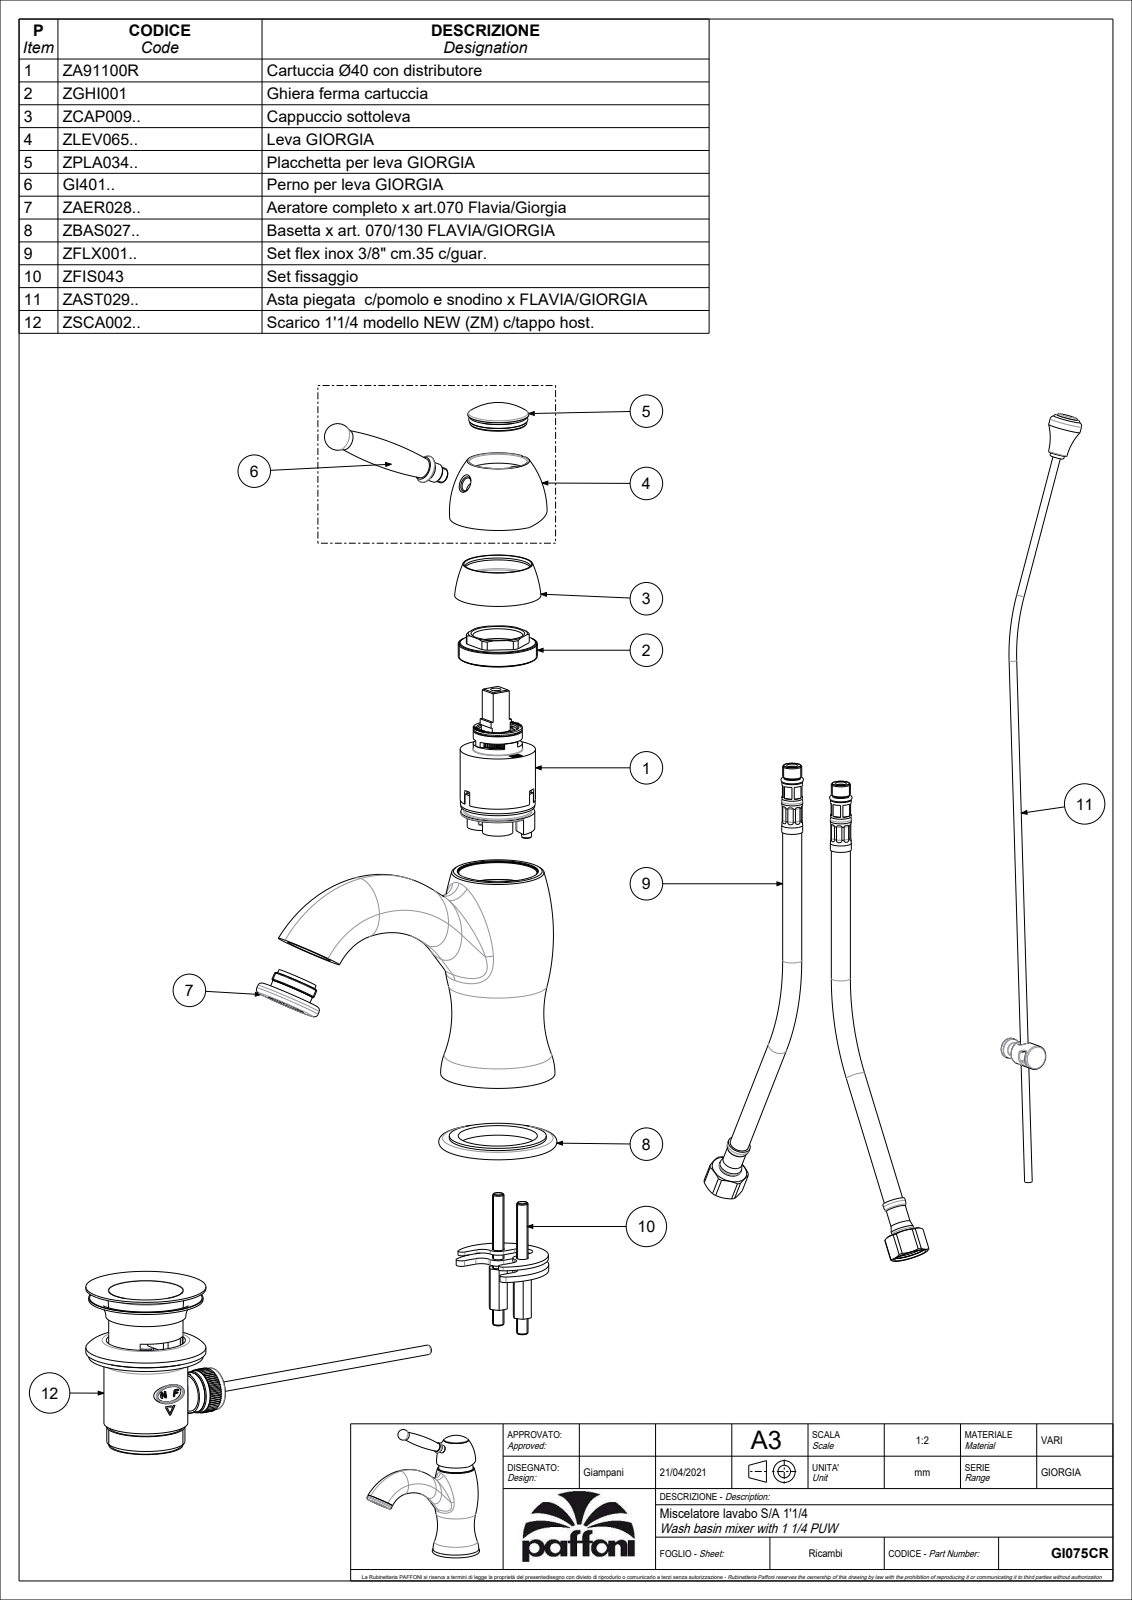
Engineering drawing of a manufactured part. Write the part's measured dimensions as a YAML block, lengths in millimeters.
part_name: "GI075CR"
step_written_by: "CREO PARAMETRIC BY PTC INC, 2020044 (CONFIG_CONTROL_DESIGN)"
units: millimeters
bodies: {solids: 3, faces: 344, planar: 85, cylindrical: 98, other: 161}
overall_size: [185.29, 179.37, 62]
volume: 185842
surface_area: 103906
round_holes:
  - {diameter: 5.5, count: 5}
  - {diameter: 5, count: 4}
  - {diameter: 9, count: 2}
  - {diameter: 11, count: 2}
  - {diameter: 12, count: 1}
  - {diameter: 16, count: 1}
  - {diameter: 20.1, count: 1}
  - {diameter: 21.1, count: 1}
  - {diameter: 23, count: 1}
  - {diameter: 30.3, count: 1}
  - {diameter: 34.5, count: 1}
  - {diameter: 39.1, count: 1}
round_bosses_or_shafts:
  - {diameter: 8.5, count: 2}
  - {diameter: 50.9, count: 1}
  - {diameter: 35, count: 1}
  - {diameter: 32, count: 1}
  - {diameter: 29.9, count: 1}
  - {diameter: 27, count: 1}
  - {diameter: 17.5, count: 1}
  - {diameter: 17, count: 1}
partial_cylinders:
  - {radius: 2.5, count: 2}
  - {radius: 6, count: 2}
  - {radius: 8, count: 2}
  - {radius: 2, count: 1}
  - {radius: 3.5, count: 1}
  - {radius: 24.35, count: 1}
face_to_face_distances: [63.5, 5.5, 5.46, 4, 63.46, 67.5, 58, 5, 67.46, 62]
hole_center_spacings: [13.6, 2.24, 7.92, 8.6, 8.78, 11.48, 12.07, 13.43]
